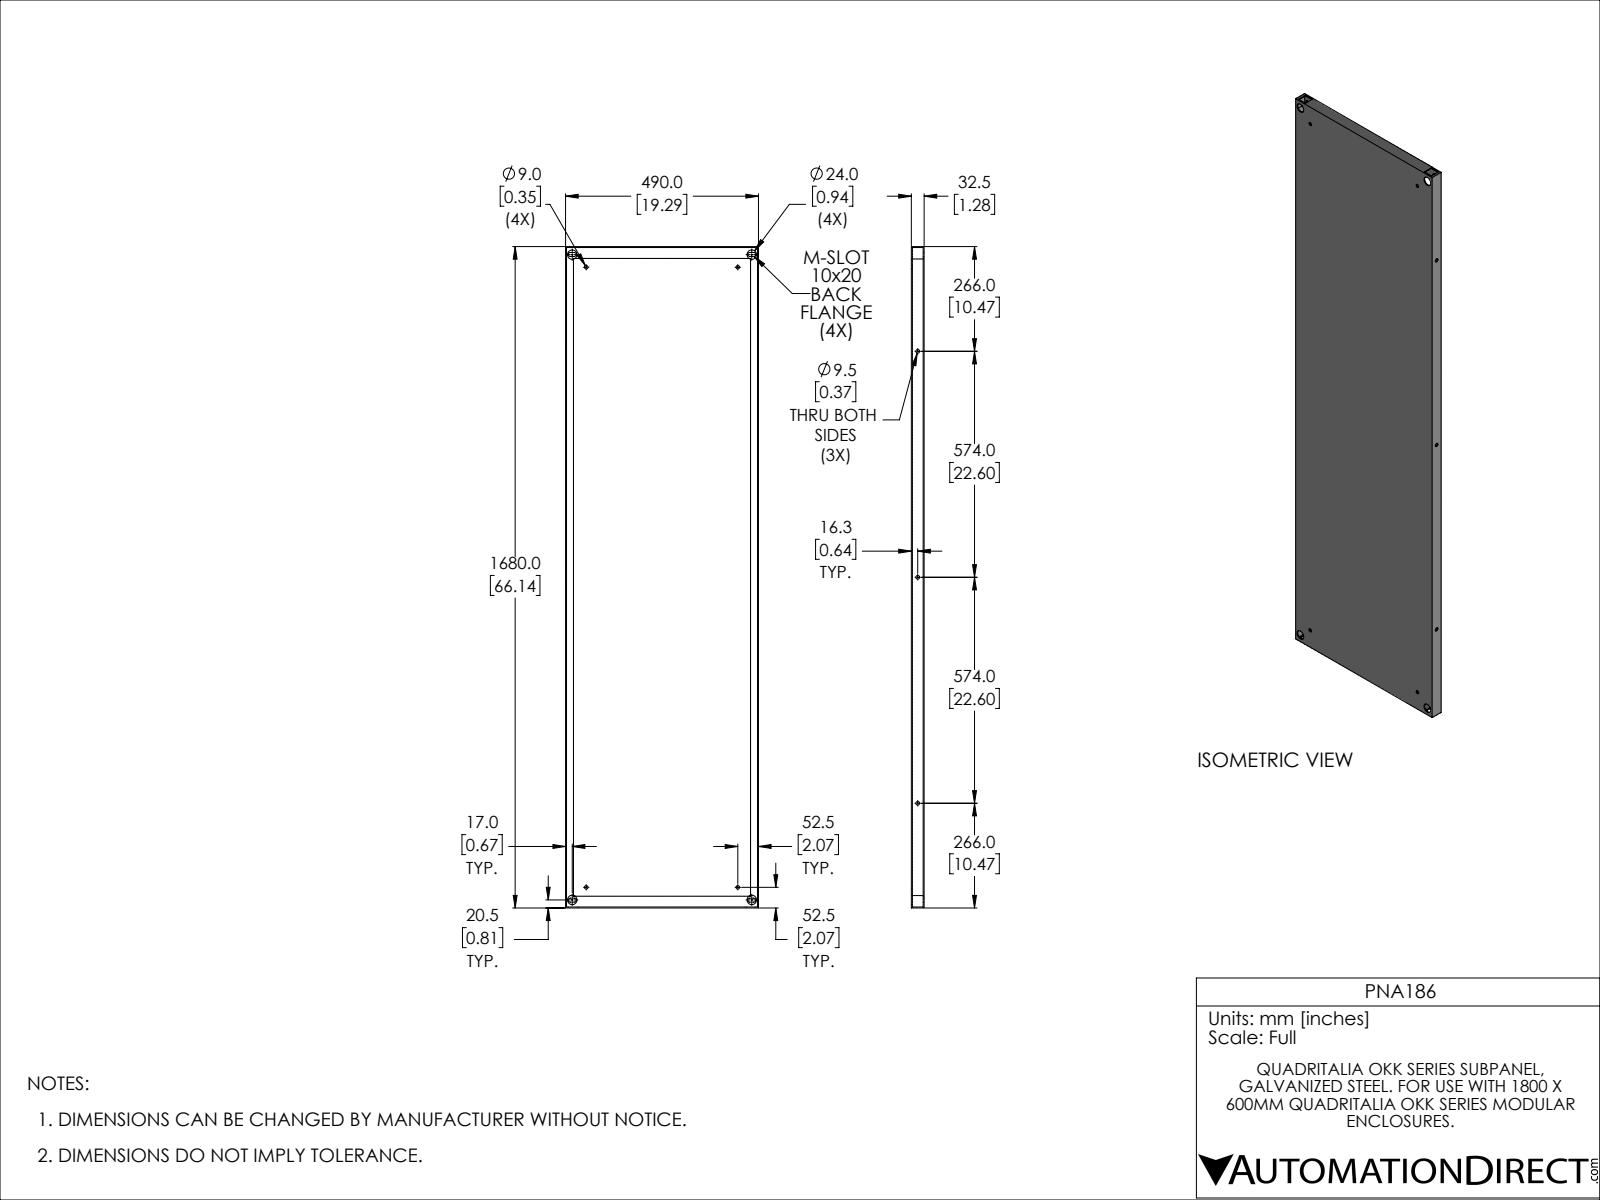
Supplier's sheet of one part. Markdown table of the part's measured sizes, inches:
| quantity | value |
| --- | --- |
| part name | PNA186 |
| STEP written by | SolidWorks 2021 (CONFIG_CONTROL_DESIGN) |
| units | inches |
| bodies | 1 solid, 70 faces (48 planar, 22 cylindrical, 0 other) |
| overall size | 66.142 × 19.291 × 1.28 |
| volume | 157.3 in³ |
| surface area | 3 216 in² |
| round holes (diameter × count) | 0.354 × 4, 0.945 × 4, 0.374 × 3 |
| partial cylindrical surfaces (radius × count) | 0.197 × 8 |
| main face-to-face distances | 0.098, 1.181, 1.28, 19.193, 1.083, 19.291, 19.094, 66.043, 66.142, 65.945 |
| hole center spacings | 1.881, 16.603, 63.283, 65.398, 15.157, 17.953, 22.598, 62.008 |
